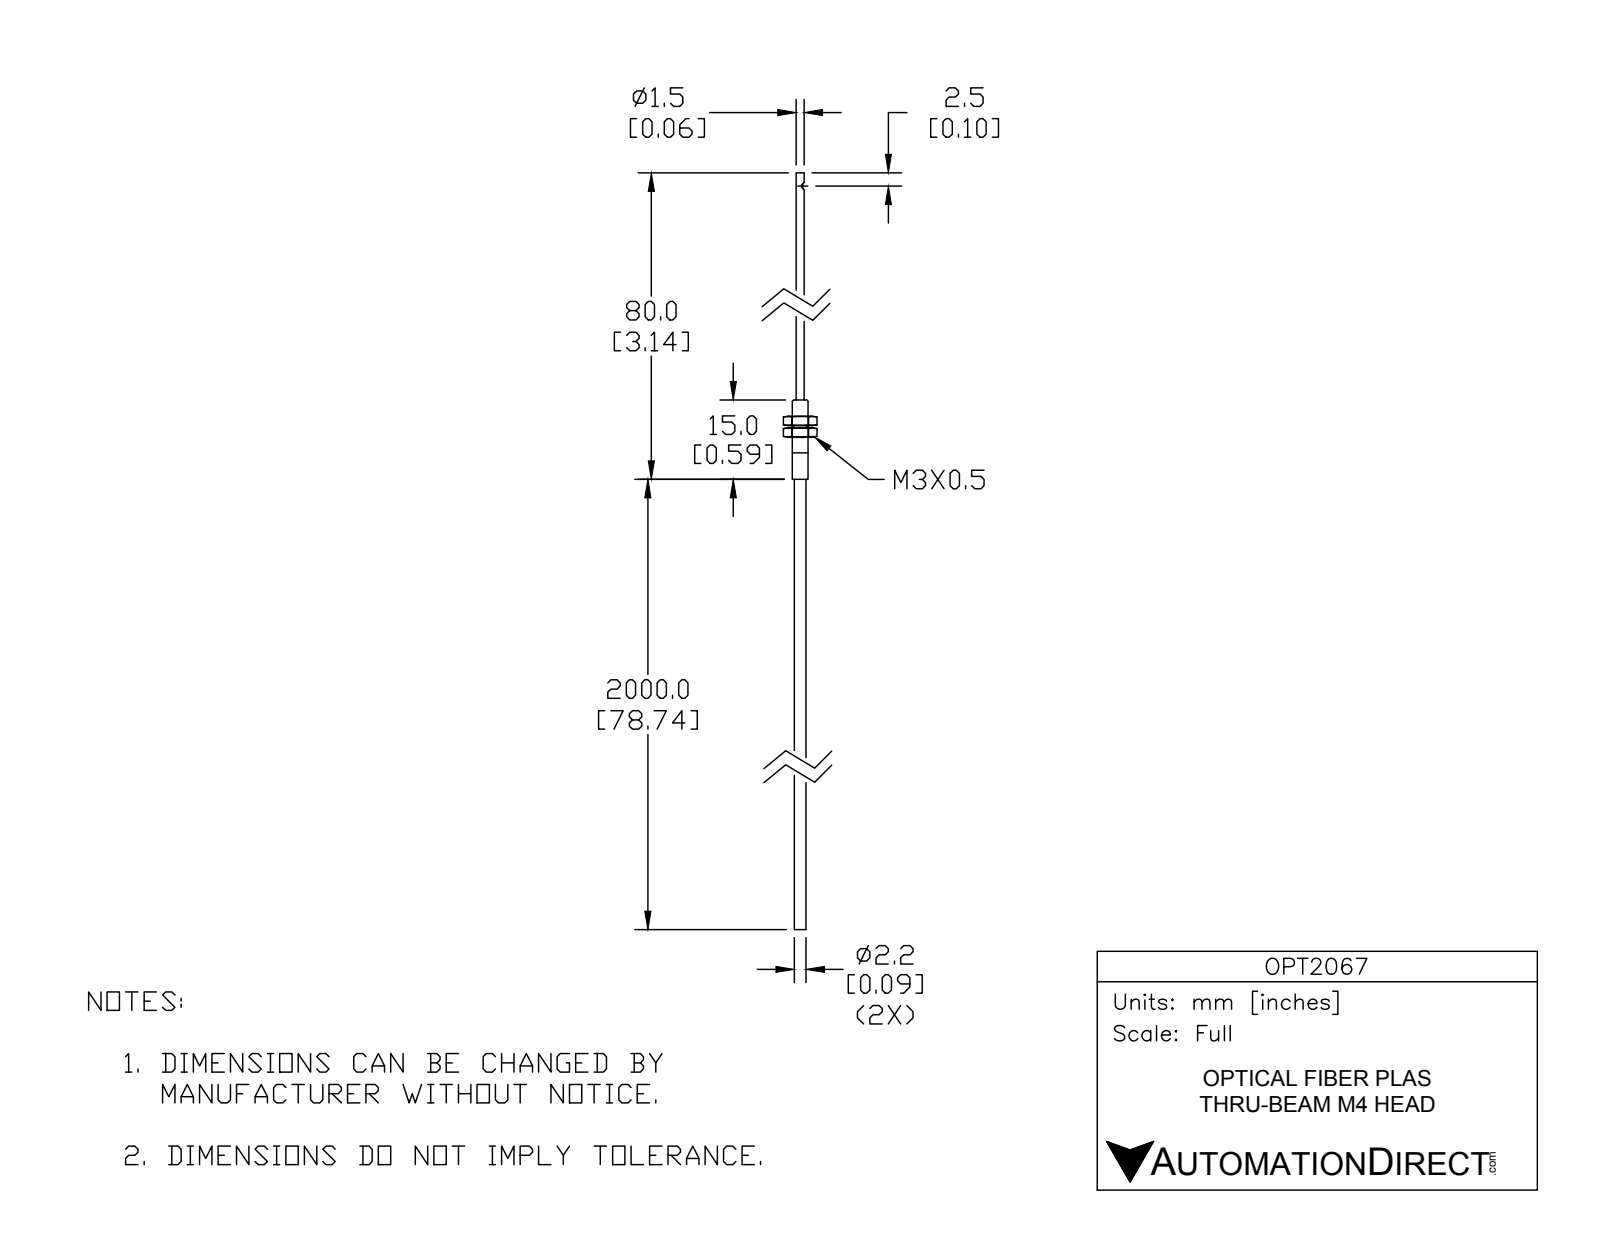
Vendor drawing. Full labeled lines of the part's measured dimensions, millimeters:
Part name (STEP PRODUCT): OPT2067
STEP written by: SolidWorks 2014 (AUTOMOTIVE_DESIGN)
Units: millimetres
Bodies: 4 solids, 60 faces (21 planar, 27 cylindrical, 12 other)
Overall size (bounding box): 165.2 × 35.1 × 3
Volume: 1 100 mm³ · Surface area: 2 032 mm²
Round bosses / shafts (diameter × count): ⌀2.2 ×6, ⌀3 ×2, ⌀1.5 ×2
Partial cylindrical surfaces — rounded edges, fillets, slot ends (radius × count): R0.5 ×2
Main face-to-face distances: 6.6, 2.8, 85.2, 100.2, 15, 40.8, 43.6, 34.2, 37, 165.2
